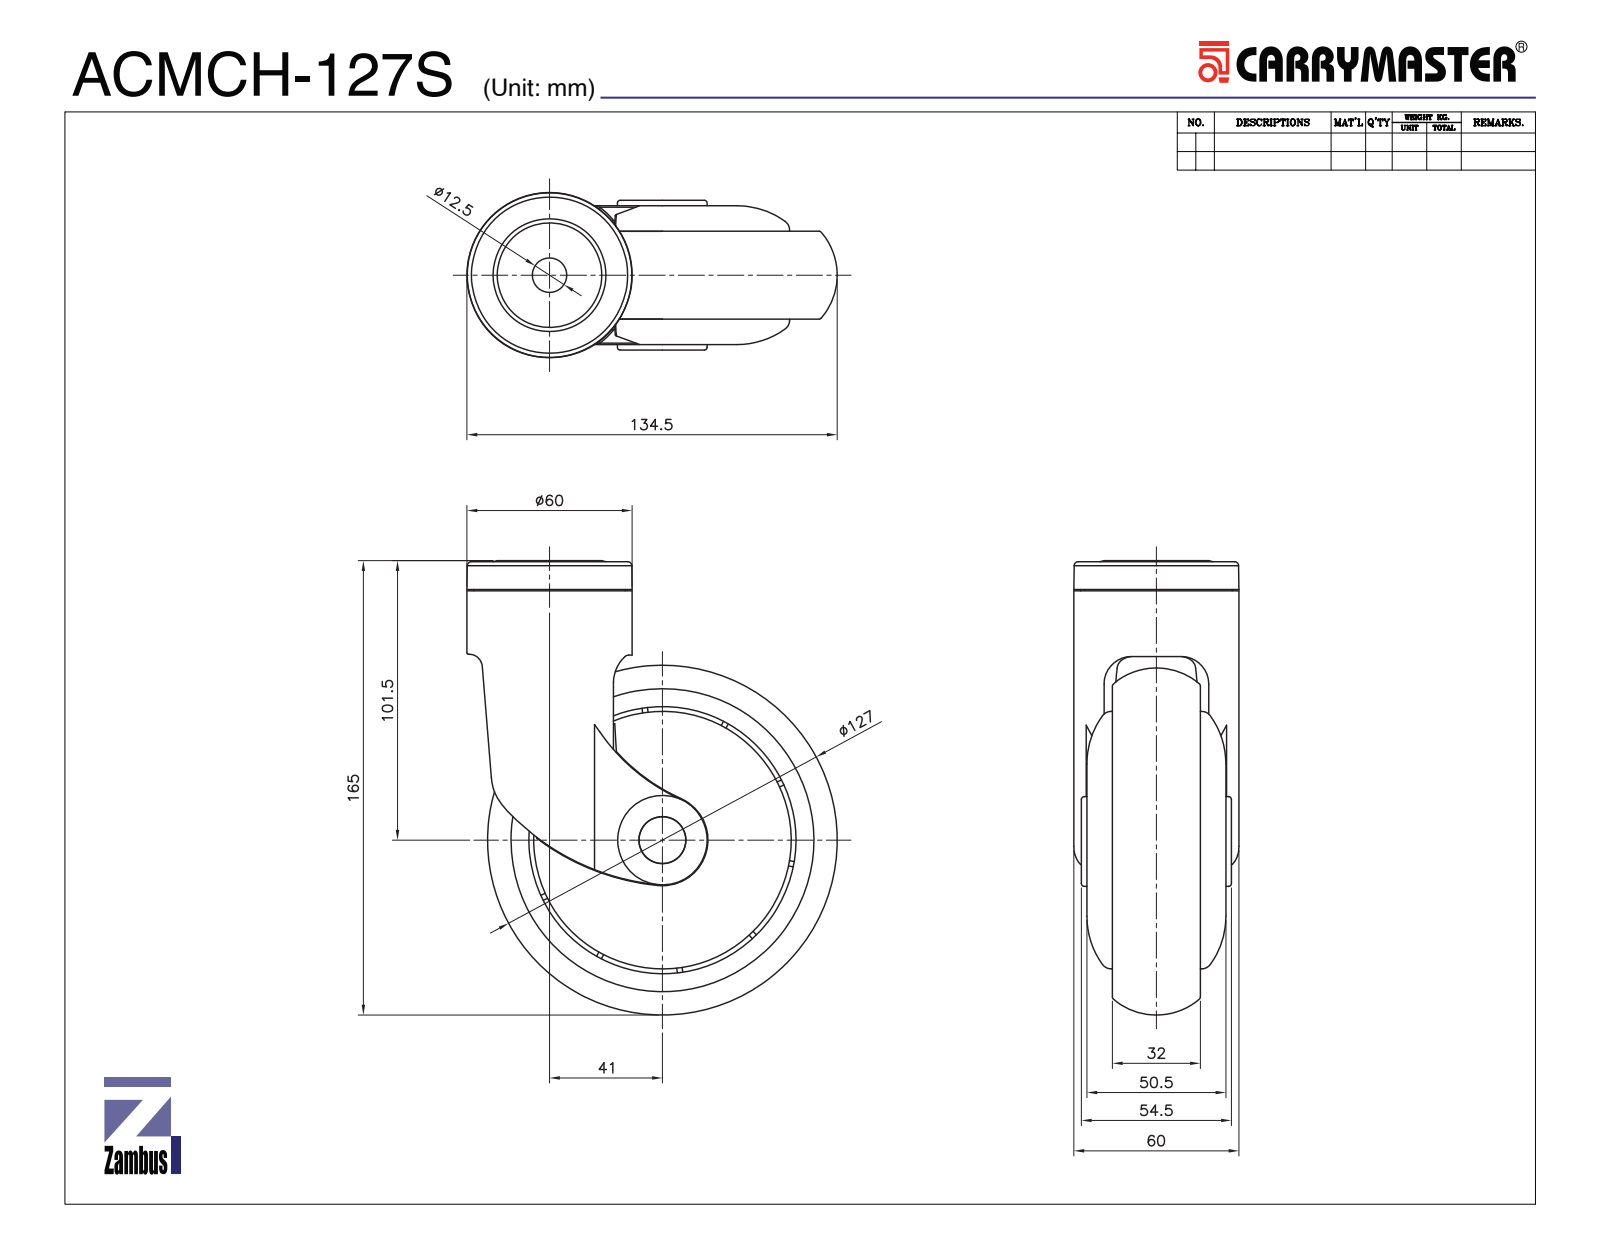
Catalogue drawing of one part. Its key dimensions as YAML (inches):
part_name: "ACMCH-127S; ACMCH-127 WHEEL; ACMCH-127 NON BRAKE FRMAE"
step_written_by: "SolidWorks 2019 (CONFIG_CONTROL_DESIGN)"
units: inches
bodies: {solids: 2, faces: 248, planar: 77, cylindrical: 98, other: 73}
overall_size: [6.496, 5.295, 2.362]
volume: 32.59
surface_area: 136.3
round_holes:
  - {diameter: 0.492, count: 1}
  - {diameter: 0.669, count: 1}
  - {diameter: 2.165, count: 1}
  - {diameter: 3.819, count: 1}
  - {diameter: 4.331, count: 1}
round_bosses_or_shafts:
  - {diameter: 4.331, count: 1}
  - {diameter: 3.681, count: 1}
  - {diameter: 2.362, count: 1}
  - {diameter: 2.087, count: 1}
  - {diameter: 1.28, count: 1}
  - {diameter: 1.181, count: 1}
  - {diameter: 0.665, count: 1}
partial_cylinders:
  - {radius: 0.02, count: 2}
  - {radius: 0.079, count: 2}
  - {radius: 0.276, count: 2}
  - {radius: 0.652, count: 1}
  - {radius: 0.925, count: 1}
  - {radius: 2.77, count: 1}
  - {radius: 2.782, count: 1}
  - {radius: 3.397, count: 1}
face_to_face_distances: [0.118, 1.378, 1.496, 0.315, 1.26, 0.433, 0.246, 0.364, 1.624, 1.742]
